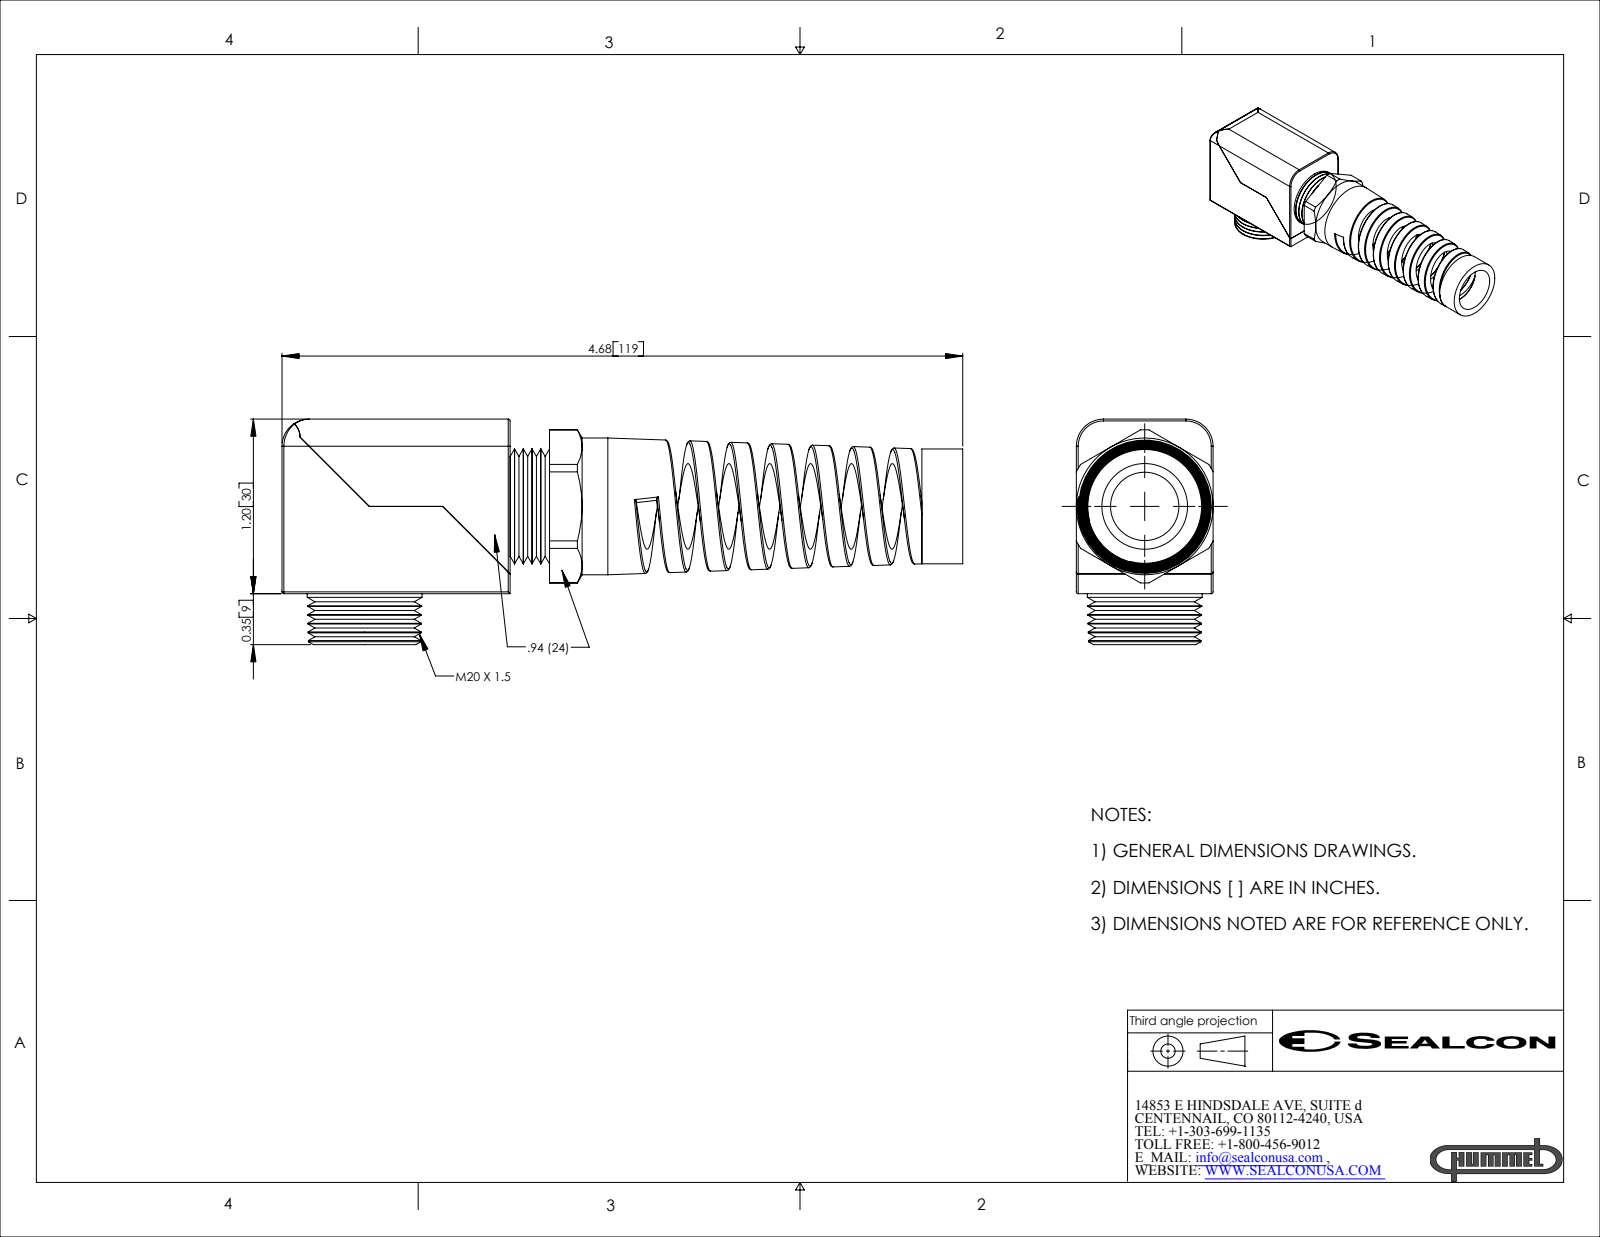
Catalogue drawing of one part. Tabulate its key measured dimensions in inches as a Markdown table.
| quantity | value |
| --- | --- |
| part name | EF20MA-GY |
| STEP written by | SolidWorks 2007 (CONFIG_CONTROL_DESIGN) |
| units | inches |
| bodies | 3 solids, 183 faces (31 planar, 63 cylindrical, 89 other) |
| overall size | 4.68 × 1.55 × 0.94 |
| volume | 2.259 in³ |
| surface area | 30.27 in² |
| round holes (diameter × count) | 0.47 × 2, 0.589 × 1, 0.632 × 1 |
| round bosses / shafts (diameter × count) | 0.94 × 1, 0.79 × 1, 0.789 × 1 |
| partial cylindrical surfaces (radius × count) | 0.013 × 8, 0.187 × 3, 0.124 × 1, 0.526 × 1 |
| main face-to-face distances | 0.94, 0.356, 0.6, 1.2, 1.568, 2.831, 4.399, 2.56, 0.271, 1.839 |
